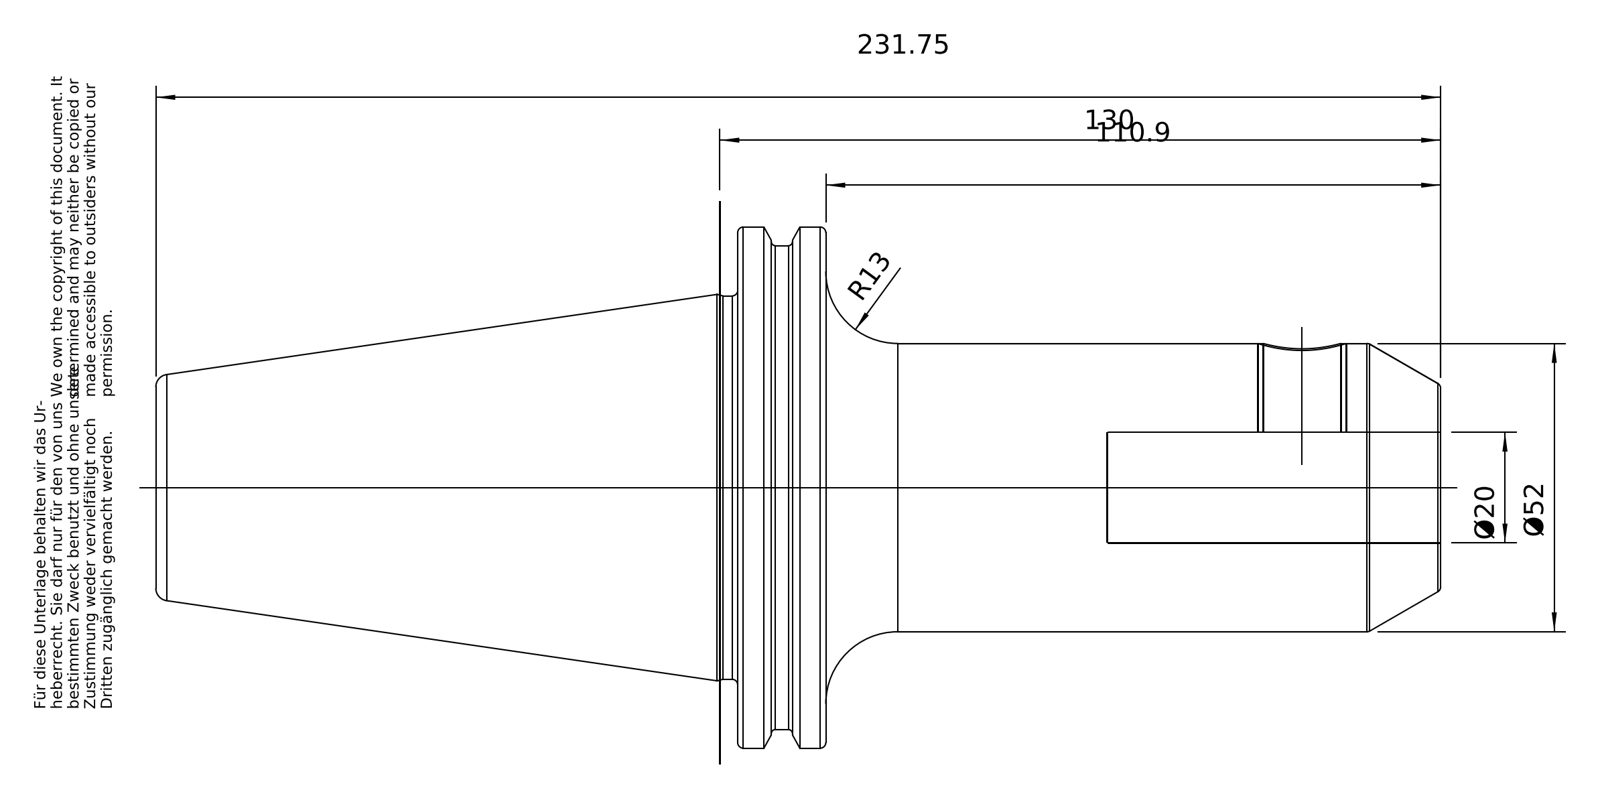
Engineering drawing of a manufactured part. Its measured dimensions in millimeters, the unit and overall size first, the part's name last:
Units: millimetres
Overall size (bounding box): 231.6 × 97.47 × 94
Round holes (diameter × count): ⌀14 ×1, ⌀16 ×1, ⌀20 ×1, ⌀20.75 ×1, ⌀25.01 ×1, ⌀25.7 ×1
Round bosses / shafts (diameter × count): ⌀91 ×1, ⌀69.15 ×1, ⌀52 ×1, ⌀24.01 ×1
Partial cylindrical surfaces — rounded edges, fillets, slot ends (radius × count): R1.75 ×5, R48.74 ×1
Main face-to-face distances: 15.85, 126.8, 110.95, 104.8, 120.65, 231.6, 72.8, 171.5, 66.7, 50.85
Volume: 552 960 mm³ · Surface area: 63 874 mm²
Bodies: 1 solid, 104 faces (22 planar, 32 cylindrical, 50 other)
Part name (STEP PRODUCT): 50-304-20
STEP written by: PRO/ENGINEER BY PARAMETRIC TECHNOLOGY CORPORATION, 2010430 (CONFIG_CONTROL_DESIGN)
